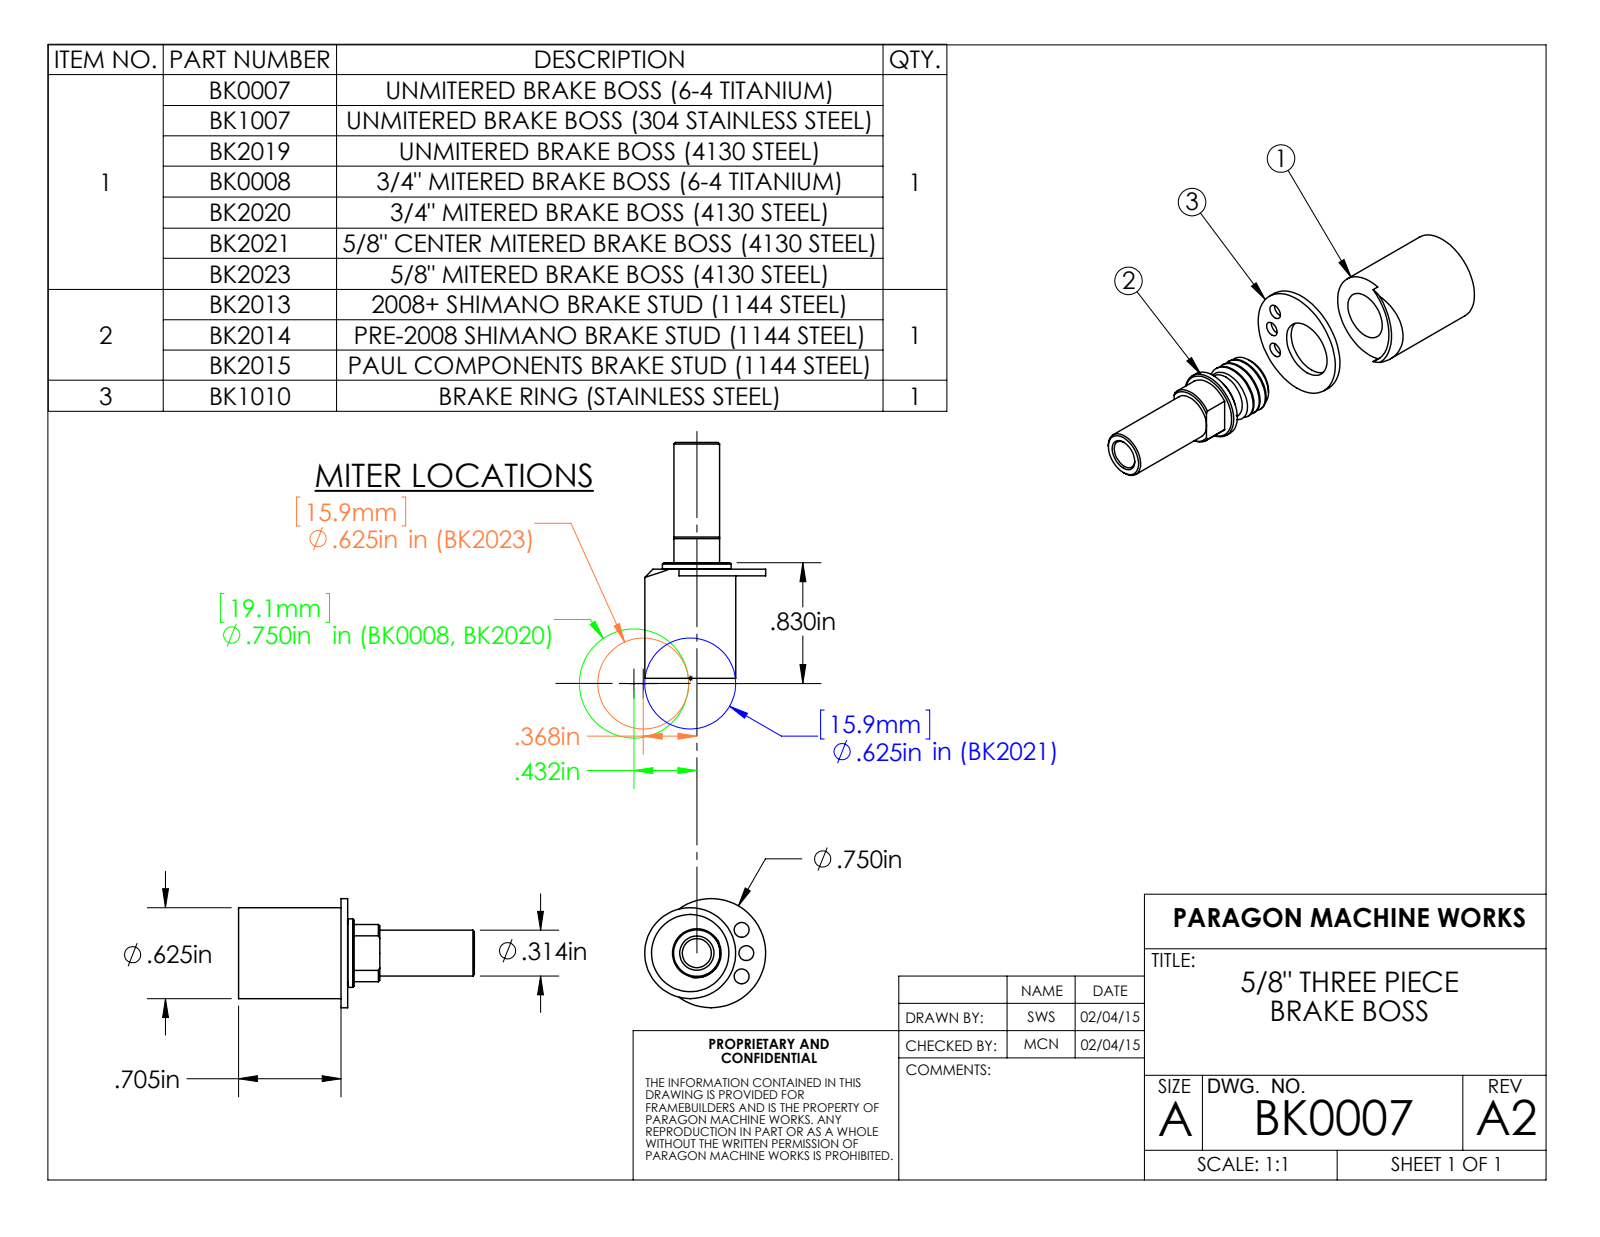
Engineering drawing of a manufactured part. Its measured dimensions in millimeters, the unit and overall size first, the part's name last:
Units: millimetres
Overall size (bounding box): 19.1 × 15.9 × 15.9
Round holes (diameter × count): ⌀10 ×1, ⌀13.2 ×1
Round bosses / shafts (diameter × count): ⌀15.9 ×1
Partial cylindrical surfaces — rounded edges, fillets, slot ends (radius × count): R9.5 ×1
Main face-to-face distances: 17.9, 12.7, 5.2, 19.1, 6.4, 1.1
Hole centre spacings: 1.2
Volume: 1 400 mm³ · Surface area: 1 857 mm²
Bodies: 1 solid, 9 faces (4 planar, 4 cylindrical, 1 other)
Part name (STEP PRODUCT): BK0007
STEP written by: SolidWorks 2012 (AUTOMOTIVE_DESIGN)
